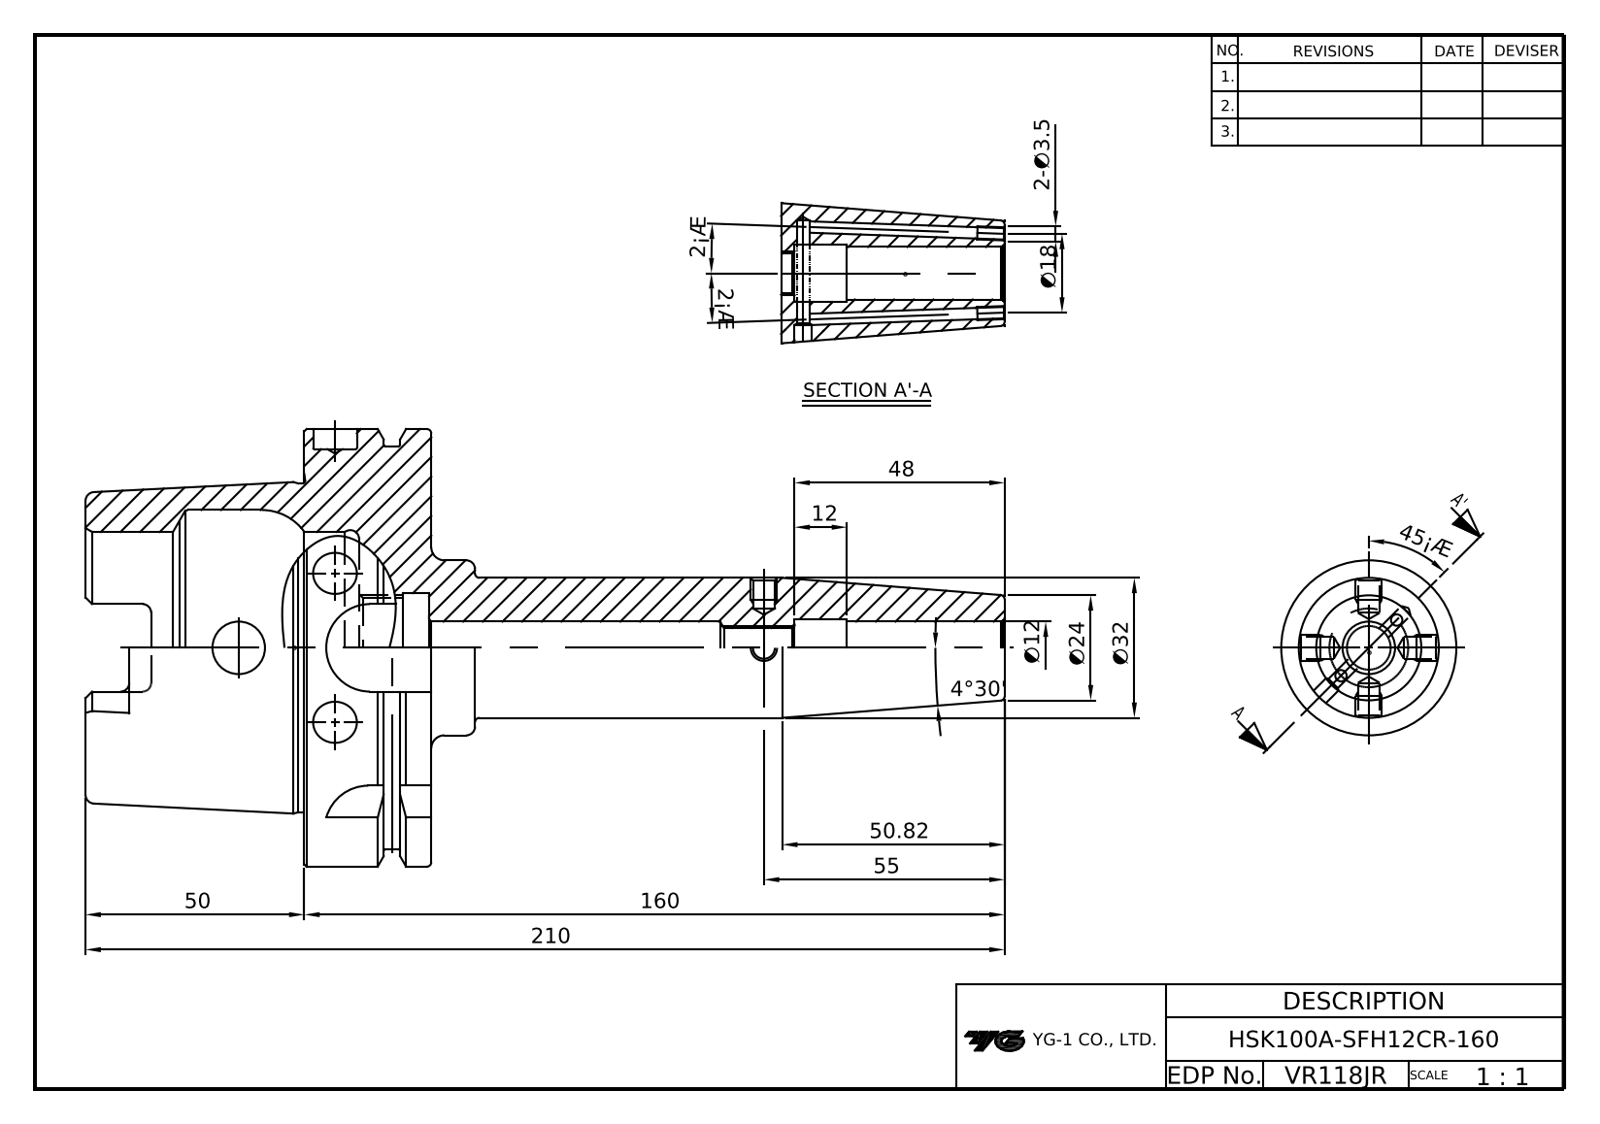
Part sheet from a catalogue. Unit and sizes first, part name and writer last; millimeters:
Units: millimetres
Overall size (bounding box): 210 × 100 × 100
Round holes (diameter × count): ⌀2.46 ×2, ⌀12 ×2, ⌀8.92 ×1, ⌀10 ×1, ⌀13.2 ×1, ⌀22.38 ×1, ⌀25 ×1, ⌀53 ×1, ⌀63 ×1
Round bosses / shafts (diameter × count): ⌀100 ×1, ⌀92 ×1, ⌀75.41 ×1, ⌀40 ×1, ⌀32 ×1
Partial cylindrical surfaces — rounded edges, fillets, slot ends (radius × count): R2 ×6, R4.88 ×4, R10 ×4
Main face-to-face distances: 29, 12.5, 16.5, 79, 62.5, 50, 10, 88, 78.5, 28.5
Volume: 340 169 mm³ · Surface area: 67 275 mm²
Bodies: 1 solid, 124 faces (39 planar, 38 cylindrical, 47 other)
Part name (STEP PRODUCT): LO-HSK100A-SFH12CR-160
STEP written by: Autodesk Inventor 2024 (AUTOMOTIVE_DESIGN)
